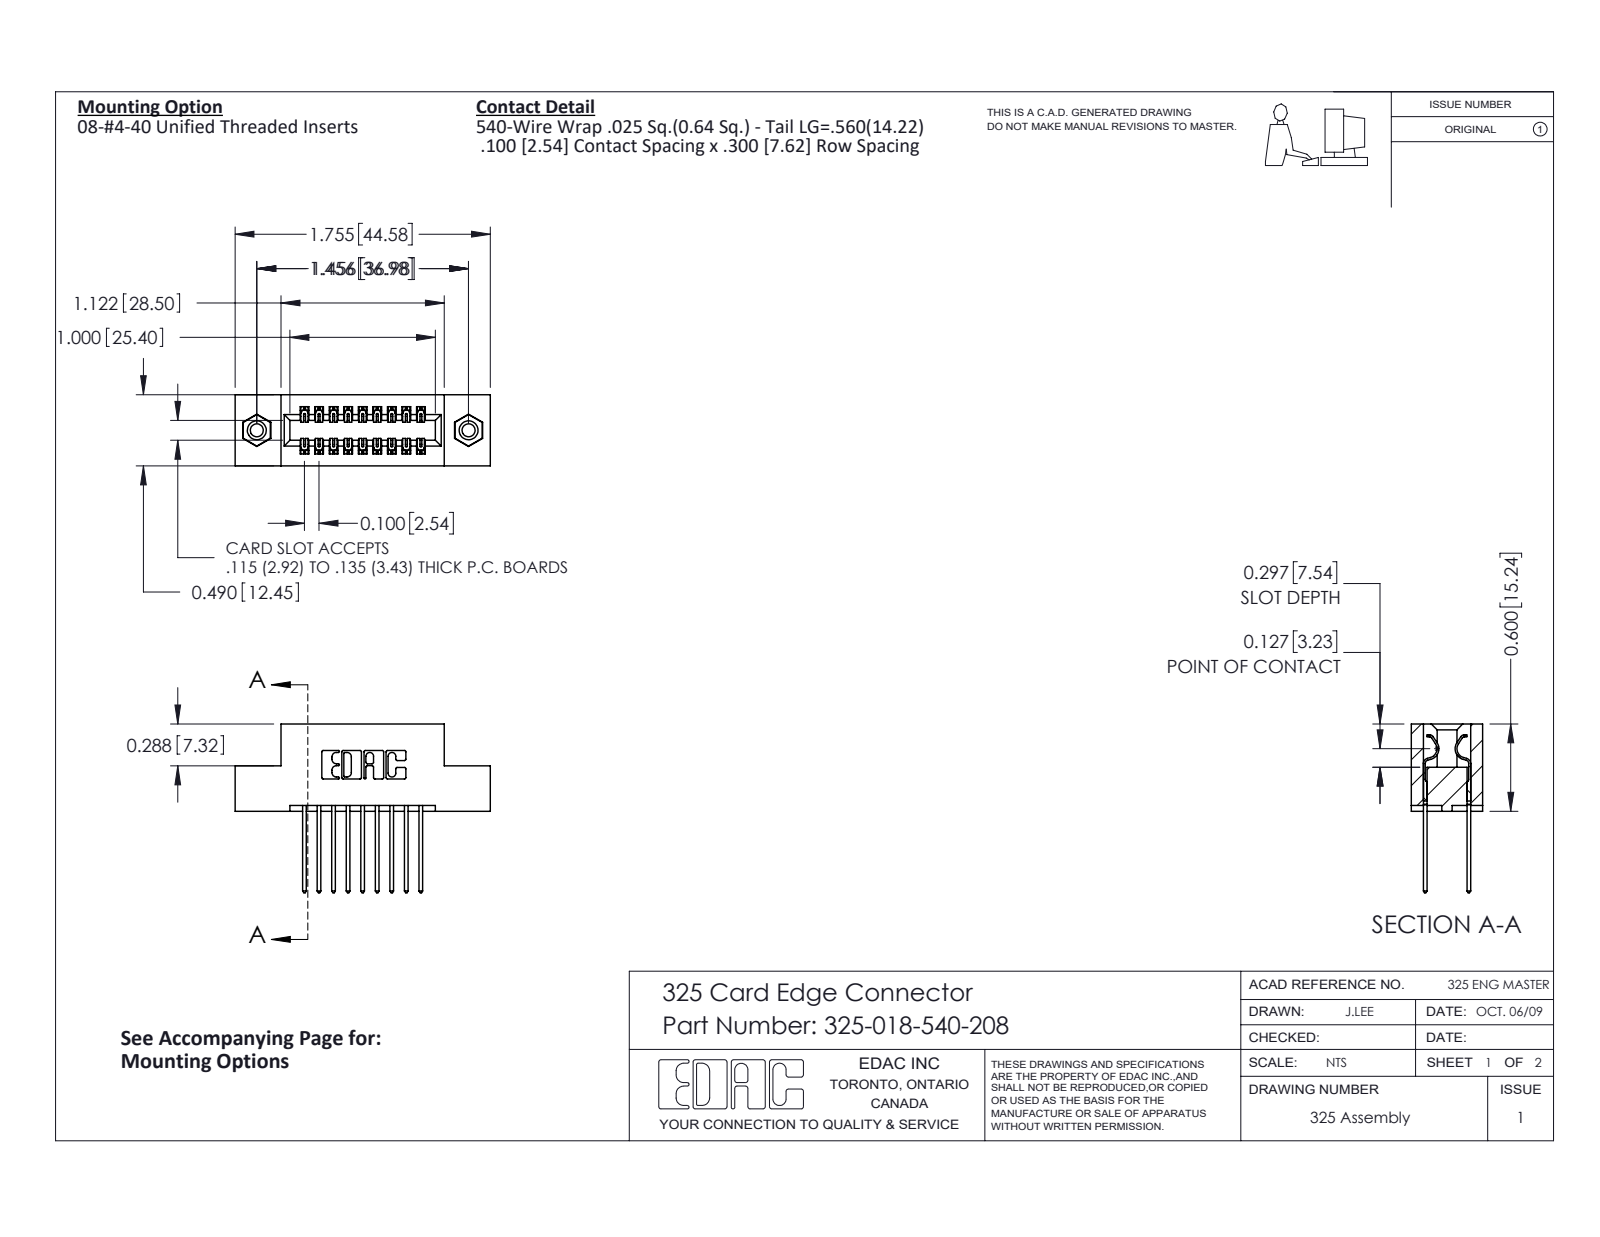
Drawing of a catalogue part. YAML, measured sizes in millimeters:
part_name: "345-250-001_345-250-003-102; 325 Part_TI; 325-018-540-208; 325-292-001_325-293-140"
step_written_by: "SolidWorks 2016 (CONFIG_CONTROL_DESIGN)"
units: millimeters
bodies: {solids: 21, faces: 1110, planar: 750, cylindrical: 344, other: 16}
overall_size: [44.6, 29.5, 12.4]
volume: 5520
surface_area: 6237
round_holes:
  - {diameter: 2.3, count: 2}
  - {diameter: 3.2, count: 2}
  - {diameter: 4.1, count: 2}
round_bosses_or_shafts:
  - {diameter: 3.9, count: 2}
partial_cylinders:
  - {radius: 0.2, count: 27}
  - {radius: 0.3, count: 22}
  - {radius: 0.3, count: 18}
  - {radius: 0.2, count: 6}
  - {radius: 0.8, count: 6}
  - {radius: 0.7, count: 3}
  - {radius: 0.4, count: 2}
  - {radius: 0.6, count: 2}
face_to_face_distances: [7.6, 2.1, 10.3, 1, 2.5, 12.4, 5.1, 2.7, 9.7, 0.6]
hole_center_spacings: [37]
